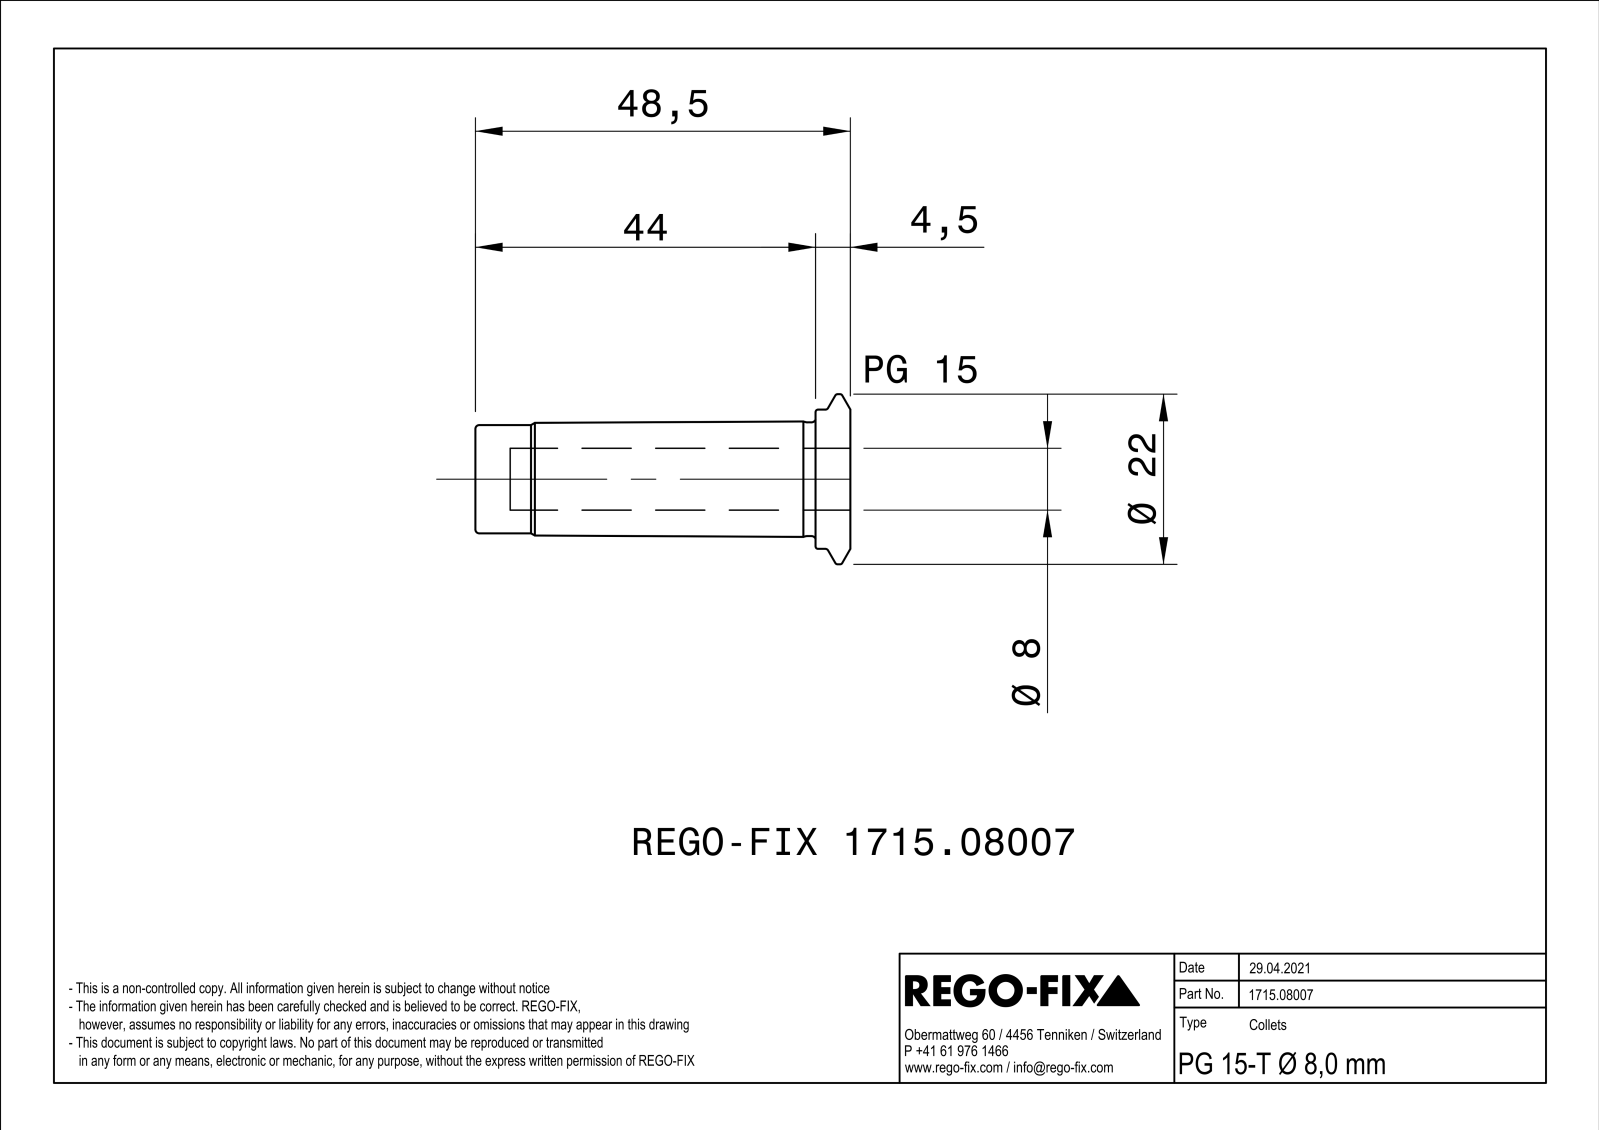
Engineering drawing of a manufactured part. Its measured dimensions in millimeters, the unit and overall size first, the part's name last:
Units: millimetres
Overall size (bounding box): 48.5 × 22 × 21.85
Round holes (diameter × count): ⌀2.46 ×1, ⌀3.3 ×1, ⌀8 ×1, ⌀8.5 ×1, ⌀11 ×1, ⌀11.4 ×1
Round bosses / shafts (diameter × count): ⌀22 ×1, ⌀18 ×1, ⌀14.7 ×1, ⌀14 ×1
Partial cylindrical surfaces — rounded edges, fillets, slot ends (radius × count): R2 ×1, R2.95 ×1, R3.01 ×1
Main face-to-face distances: 0.8, 48.5, 4.5, 44, 47.9, 43.4, 0.6, 46.8, 42.3, 1.1
Bodies: 0 solids, 85 faces (22 planar, 22 cylindrical, 41 other)
Part name (STEP PRODUCT): NOCUT
STEP written by: SIEMENS PLM Software Solid Edge ST10 (AUTOMOTIVE_DESIGN)
